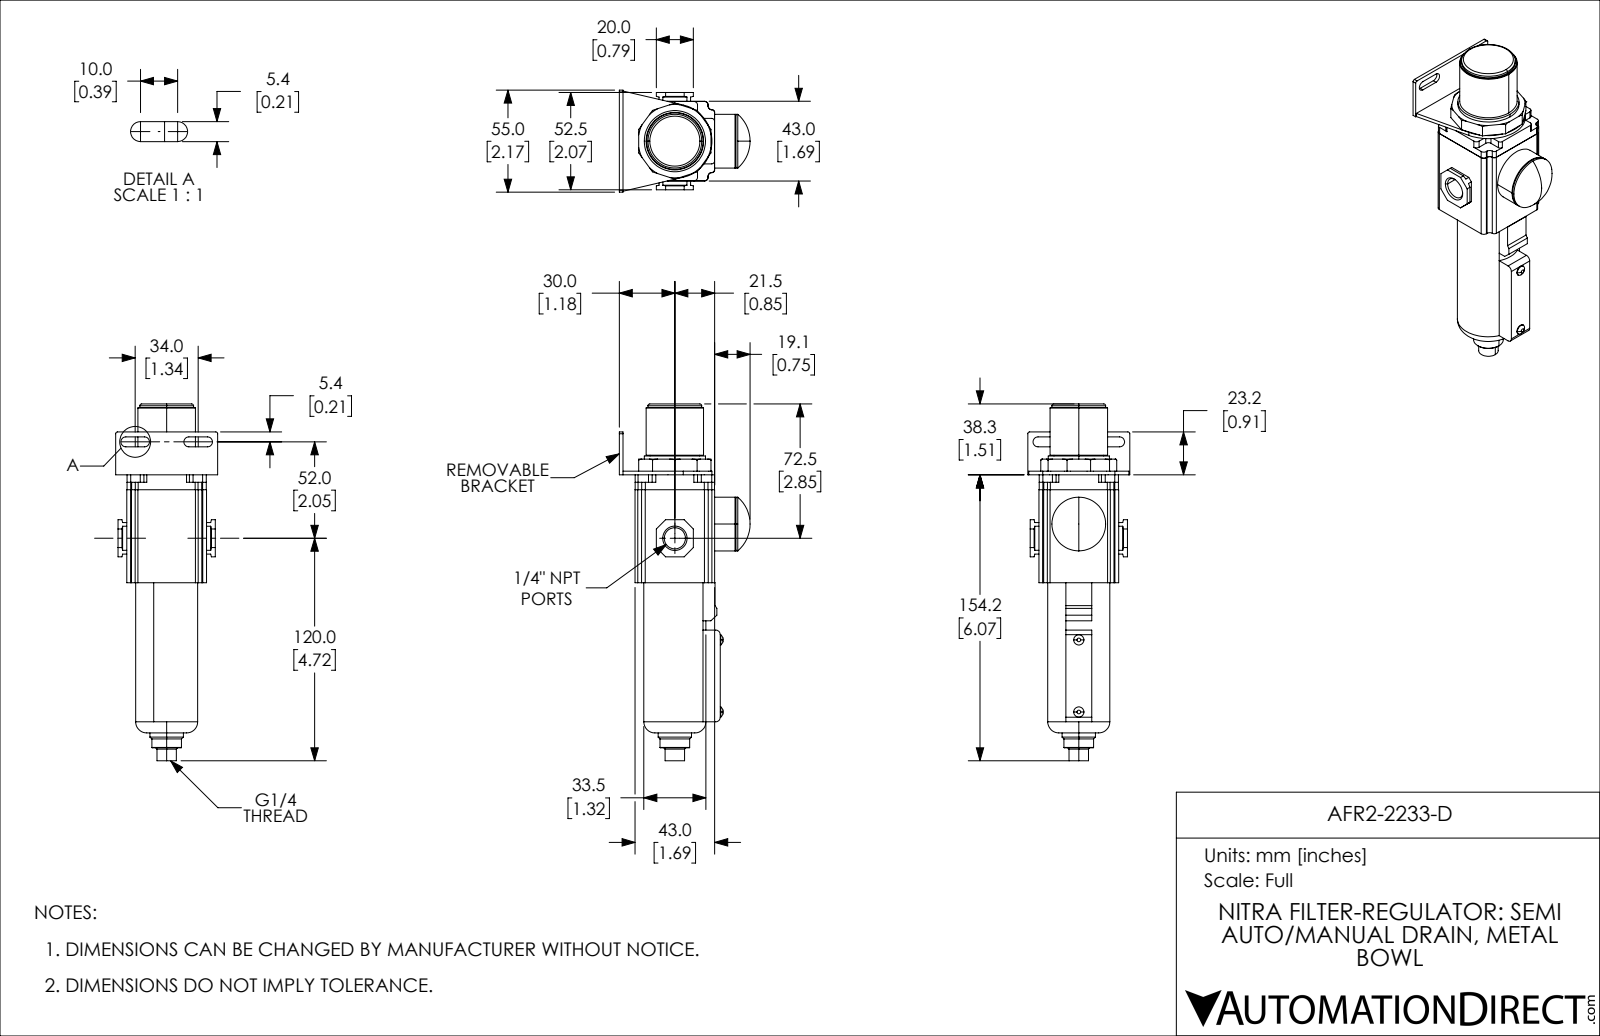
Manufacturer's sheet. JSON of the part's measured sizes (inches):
{"part_name": "AFR2-2233-D", "step_written_by": "SolidWorks 2019 (CONFIG_CONTROL_DESIGN)", "units": "inches", "bodies": {"solids": 1, "faces": 237, "planar": 126, "cylindrical": 75, "other": 36}, "overall_size": [7.579, 2.78, 2.165], "volume_in3": 14.05, "surface_area_in2": 53.48, "round_holes": [[0.163, 1], [0.451, 1]], "round_bosses_or_shafts": [[1.142, 2], [0.217, 2], [1.319, 1], [1.299, 1], [1.22, 1], [1.054, 1], [0.709, 1], [0.63, 1]], "partial_cylinders_radius": [[0.079, 24], [0.059, 12], [0.106, 4], [0.039, 2], [0.098, 2], [0.787, 1]], "face_to_face_distances": [1.693, 0.079, 0.335, 0.256, 0.571, 1.122, 1.949, 2.028, 1.689, 2.067]}
